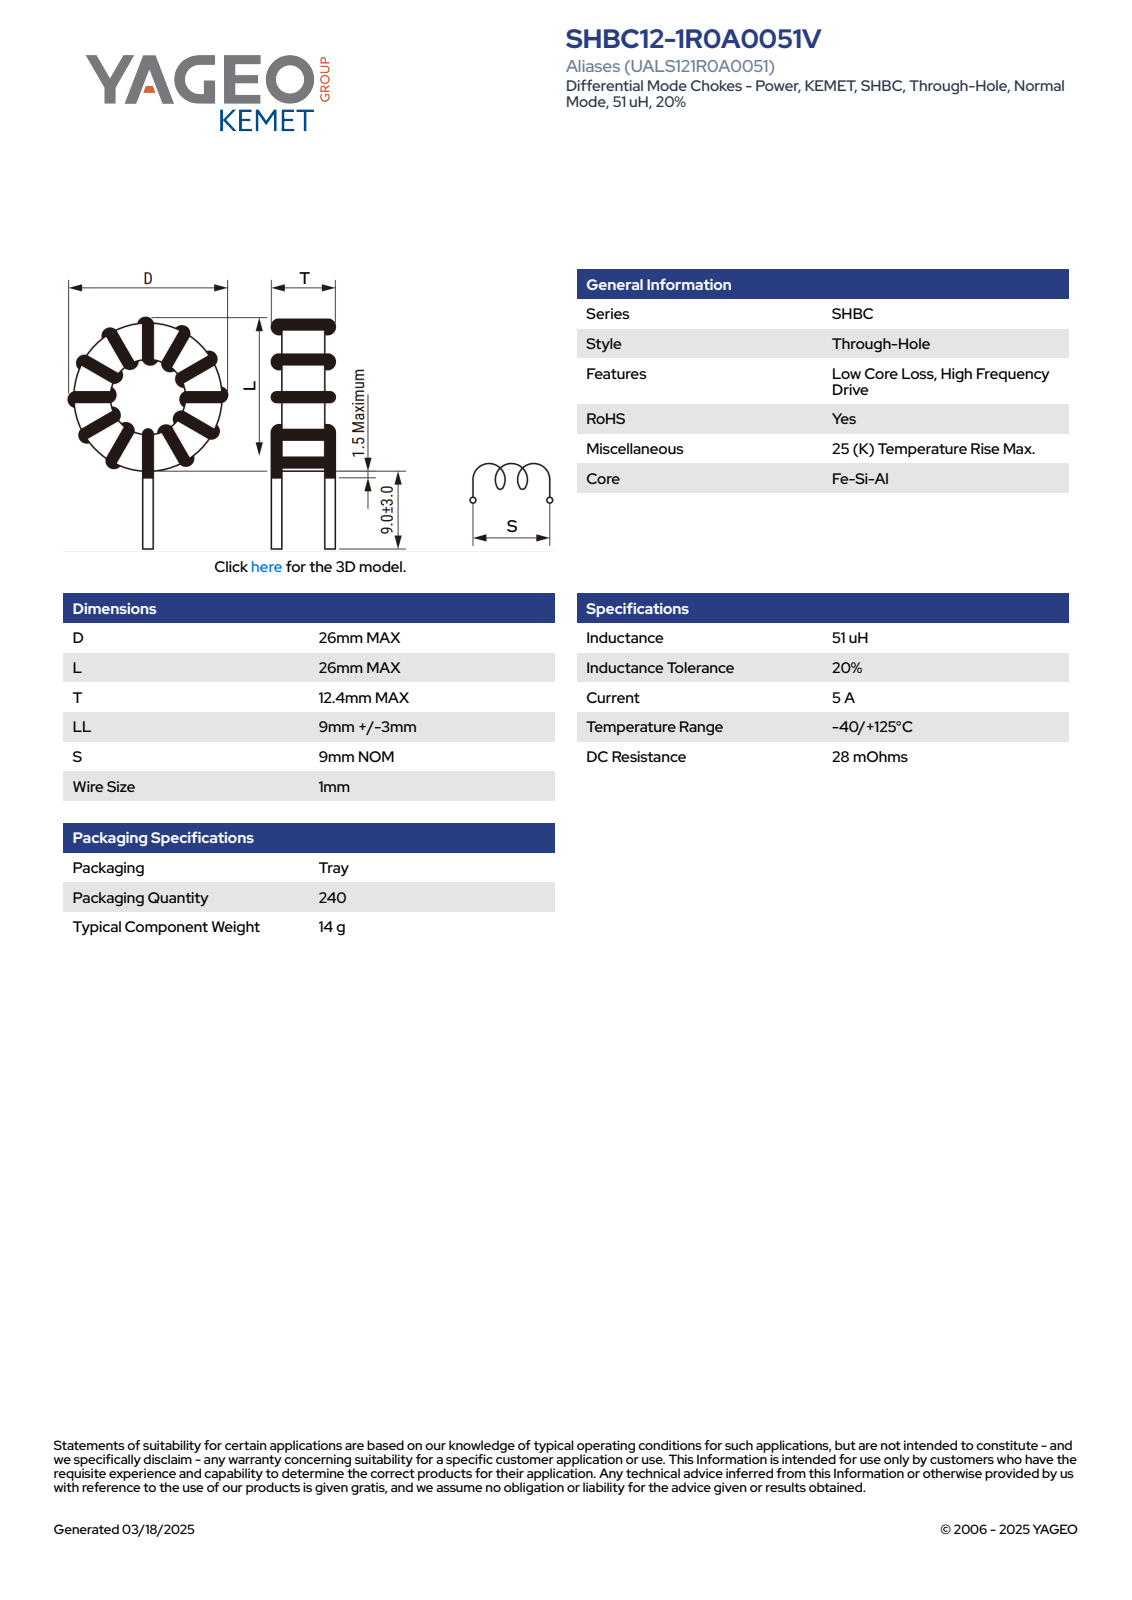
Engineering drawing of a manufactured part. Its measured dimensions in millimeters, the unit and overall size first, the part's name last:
Units: millimetres
Overall size (bounding box): 35 × 26 × 12.4
Round holes (diameter × count): ⌀11.39 ×1
Round bosses / shafts (diameter × count): ⌀1 ×3, ⌀26 ×1
Partial cylindrical surfaces — rounded edges, fillets, slot ends (radius × count): R0.5 ×8, R6.04 ×1, R10.55 ×1, R13 ×1
Main face-to-face distances: 12.4, 2.64, 9.76, 4.7, 7.7, 2.06, 5.06, 7.12, 3
Volume: 5 233 mm³ · Surface area: 2 409 mm²
Bodies: 1 solid, 80 faces (14 planar, 42 cylindrical, 24 other)
Part name (STEP PRODUCT): SHBC12-1R0A0051V
STEP written by: SolidWorks 2018 (AUTOMOTIVE_DESIGN)
